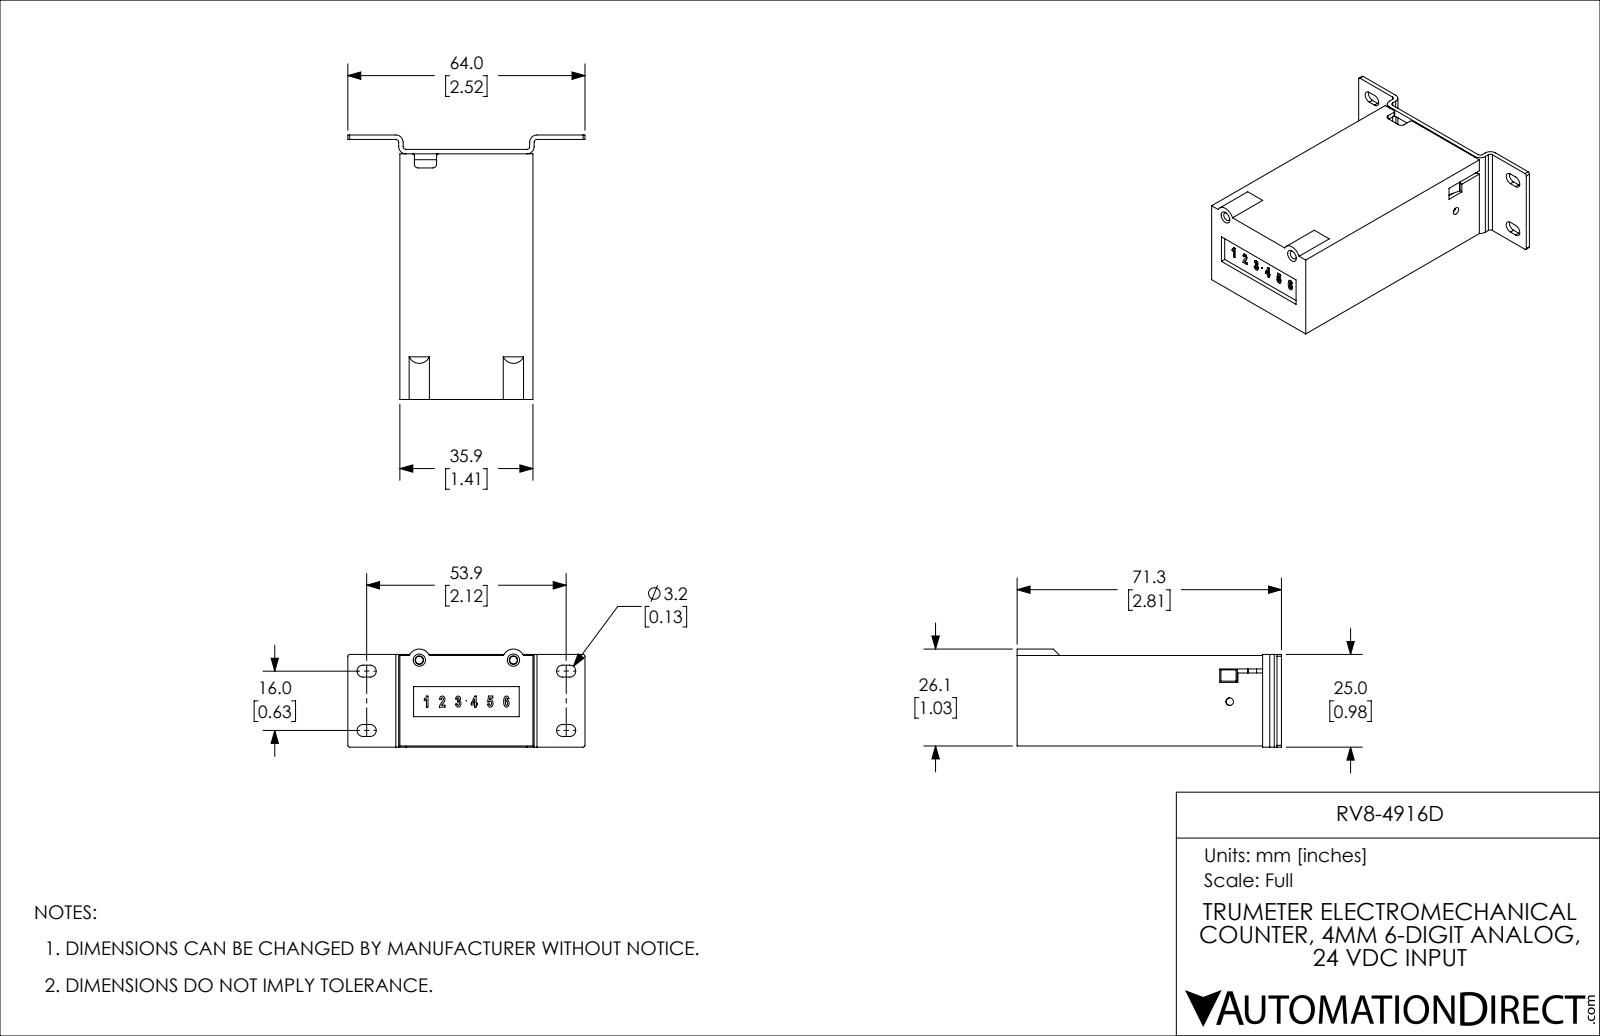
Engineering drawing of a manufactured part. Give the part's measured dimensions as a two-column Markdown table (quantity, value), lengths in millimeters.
| quantity | value |
| --- | --- |
| part name | RV8-4916D |
| STEP written by | SolidWorks 2021 (CONFIG_CONTROL_DESIGN) |
| units | millimeters |
| bodies | 1 solid, 354 faces (219 planar, 104 cylindrical, 31 other) |
| overall size | 71.33 × 64 × 26.46 |
| volume | 18 281 mm³ |
| surface area | 26 612 mm² |
| round holes (diameter × count) | 2.02 × 5, 3.17 × 2, 4 × 2, 2.01 × 1, 2.03 × 1, 2.46 × 1, 2.46 × 1, 3.12 × 1, 5.6 × 1 |
| round bosses / shafts (diameter × count) | 6 × 2 |
| partial cylindrical surfaces (radius × count) | 0.5 × 11, 1 × 10, 1.6 × 8, 0.75 × 4, 1.95 × 4, 0.25 × 2, 0.3 × 2, 1.5 × 2 |
| main face-to-face distances | 1.6, 1.35, 34.55, 2.95, 32.95, 31.6, 24.39, 35.9, 33.2, 30 |
| hole center spacings | 13.21, 25.86, 26.65, 26.67, 4.75, 5, 7.03, 8.14 |
